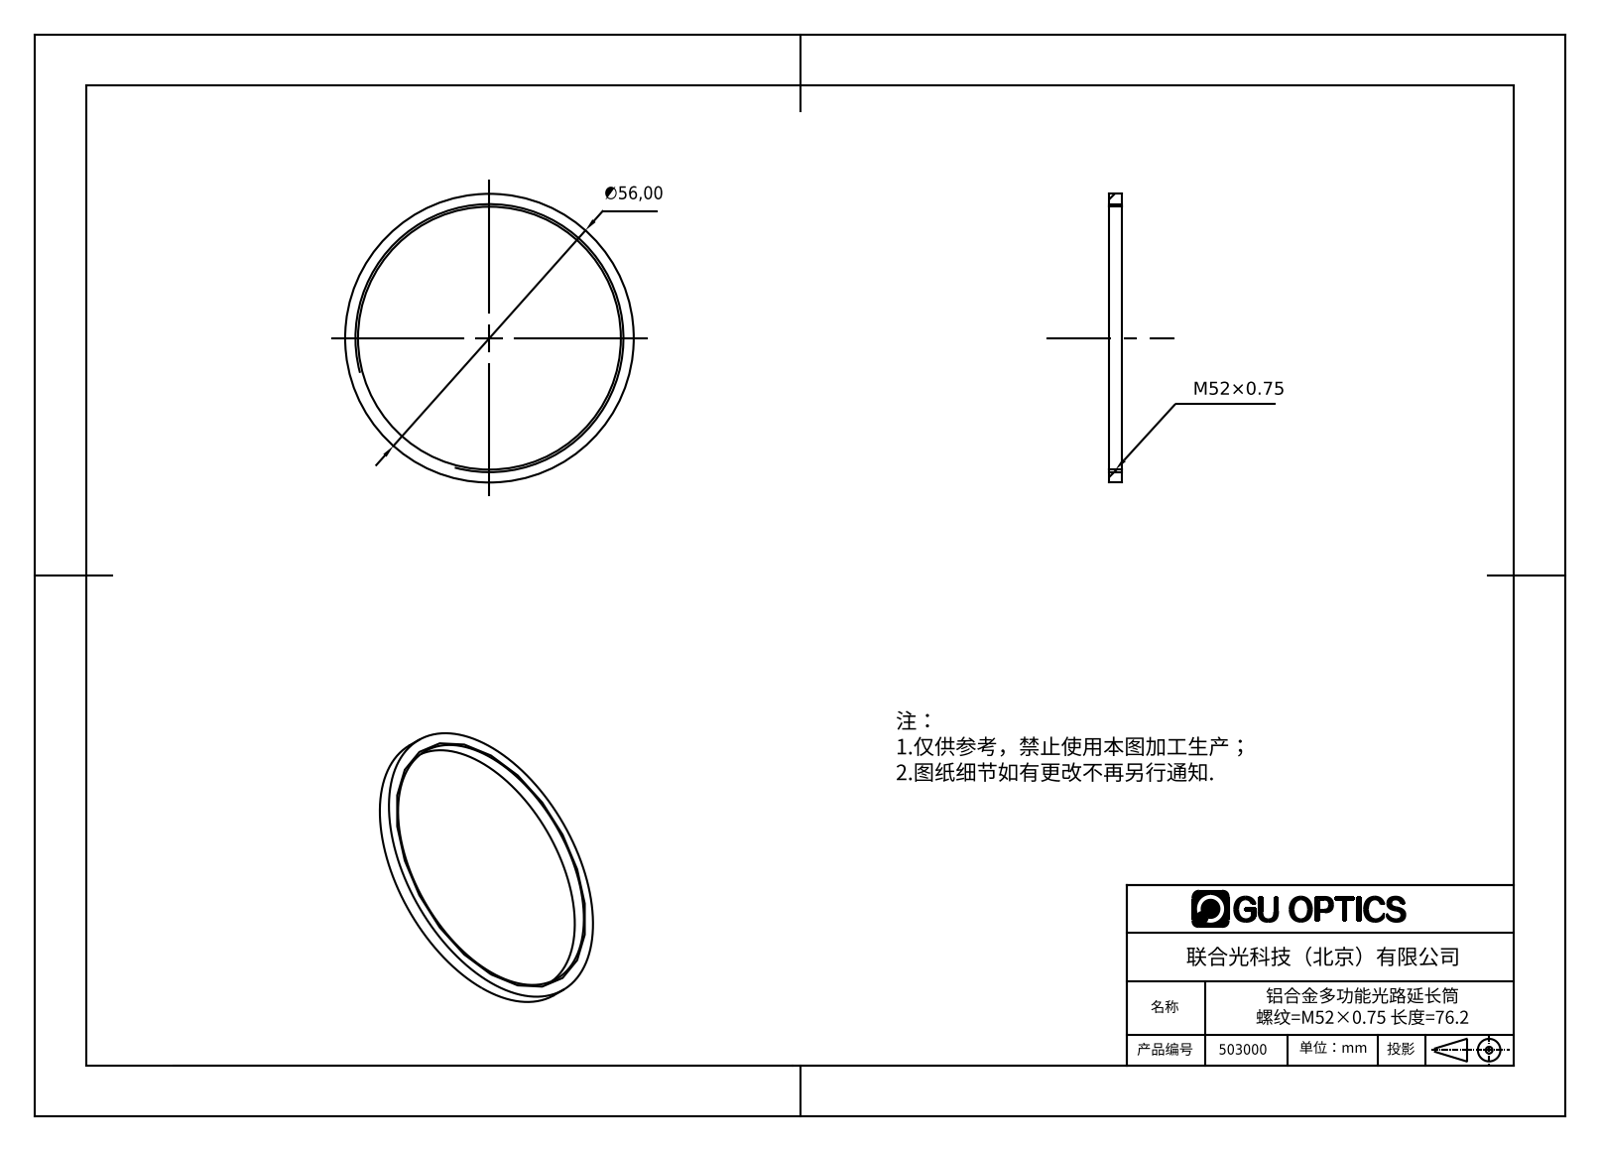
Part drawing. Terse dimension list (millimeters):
name: 511000
written by: SolidWorks 2016 (AUTOMOTIVE_DESIGN)
unit: mm
bodies: 1 solid, 6 faces (2 planar, 4 cylindrical, 0 other)
size: 56 × 56 × 2.5
volume: 1 050 mm³; area: 1 681 mm²
holes: 1× ⌀51
bosses: 1× ⌀56
face distances: 2.5
